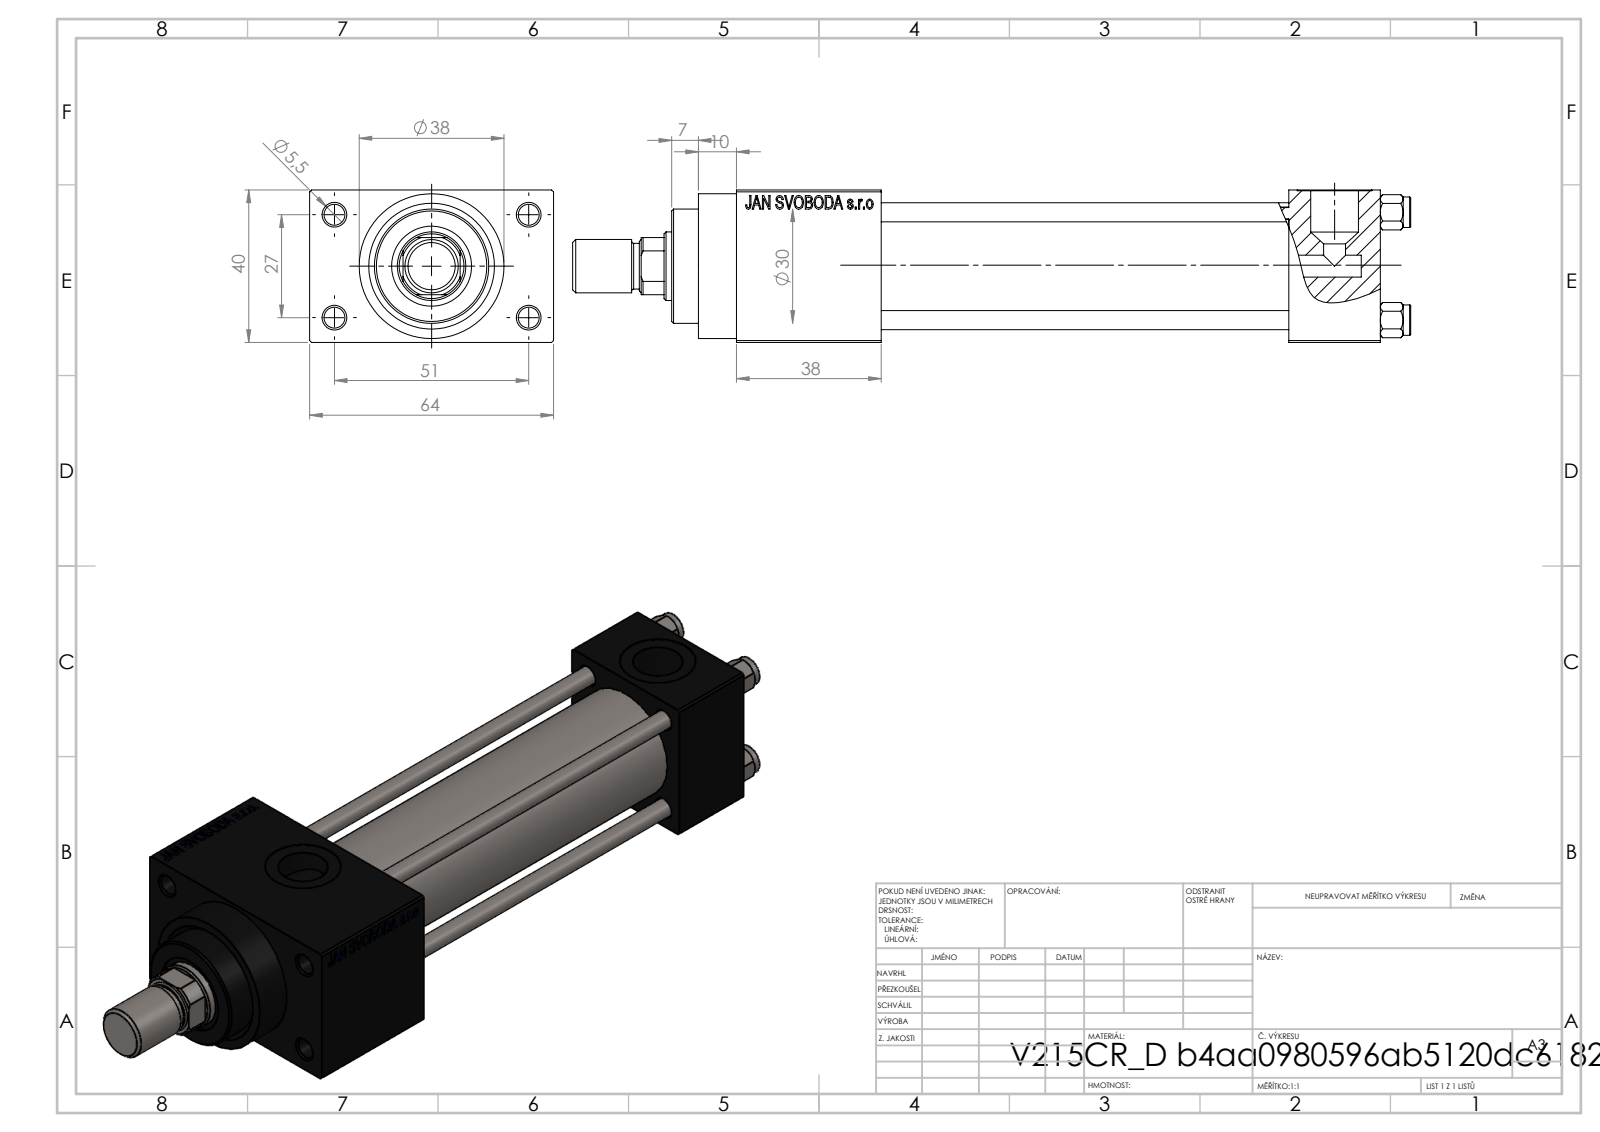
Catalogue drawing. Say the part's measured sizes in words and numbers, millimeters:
The part is named "V215CR_VCP_D; V215CR_D_TYCINKA; V215_VC_A; ROD_END_AH (+2 more)". Its 3-D file was written by "SolidWorks 2019 (CONFIG_CONTROL_DESIGN)". It is 12 solids with 1116 faces: 499 planar, 91 cylindrical and 526 other. Overall it measures 220 by 64 by 40 millimeters. Its volume is 219 160 cubic millimeters and its surface area 82 979 square millimeters. Round holes: 4 of diameter 5, 4 of diameter 5.5, 3 of diameter 20, 2 of diameter 7, 2 of diameter 13.16, 1 of diameter 8.5, 1 of diameter 18, 1 of diameter 21, 1 of diameter 25, 1 of diameter 30. Round bosses or shafts: 4 of diameter 8, 1 of diameter 38, 1 of diameter 31, 1 of diameter 14, 1 of diameter 12. Partial cylindrical surfaces (rounded edges, fillets, slot ends): 1 of radius 8.5. The main face-to-face distances are 40, 12, 52, 107, 24, 131, 64, 38, 169, 145. The hole center spacings are 11.37, 20.01, 28.3, 28.85, 29.89, 39.66, 48.34, 27.
